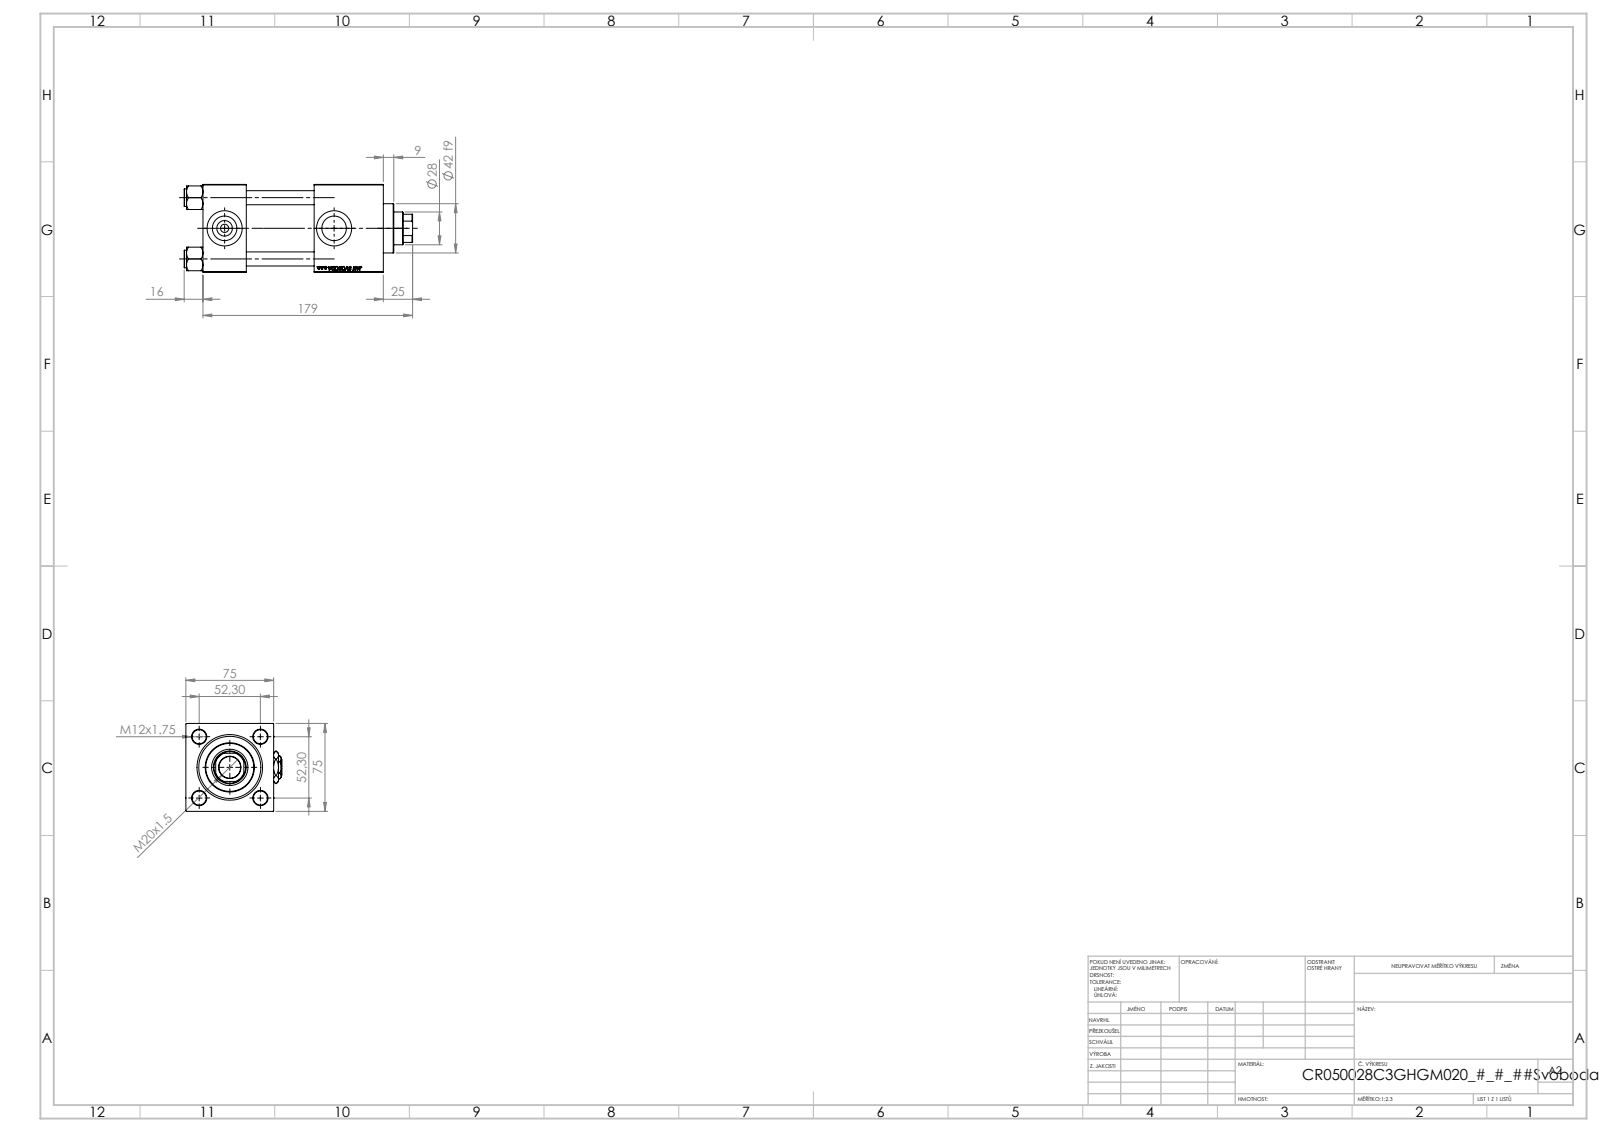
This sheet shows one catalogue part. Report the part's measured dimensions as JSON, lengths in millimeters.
{"part_name": "NUT_M5_C; V215CR_VCP_C; V215_VC_A; V215CR_C_TYCINKA (+2 more)", "step_written_by": "SolidWorks 2019 (CONFIG_CONTROL_DESIGN)", "units": "millimeters", "bodies": {"solids": 13, "faces": 1249, "planar": 573, "cylindrical": 98, "other": 578}, "overall_size": [195, 82.27, 75], "volume_mm3": 663959, "surface_area_mm2": 155409, "round_holes": [[12, 4], [7, 2], [20.96, 2], [30, 2], [18.5, 1], [28, 1], [31, 1], [41, 1], [50, 1], [53, 1]], "round_bosses_or_shafts": [[15, 4], [56, 1], [42, 1]], "partial_cylinders_radius": [[13.5, 1]], "face_to_face_distances": [75, 37, 154, 117, 95, 58, 59, 125.3, 88.3, 30.3], "hole_center_spacings": [36.98, 52.3, 73.96, 93.5]}
